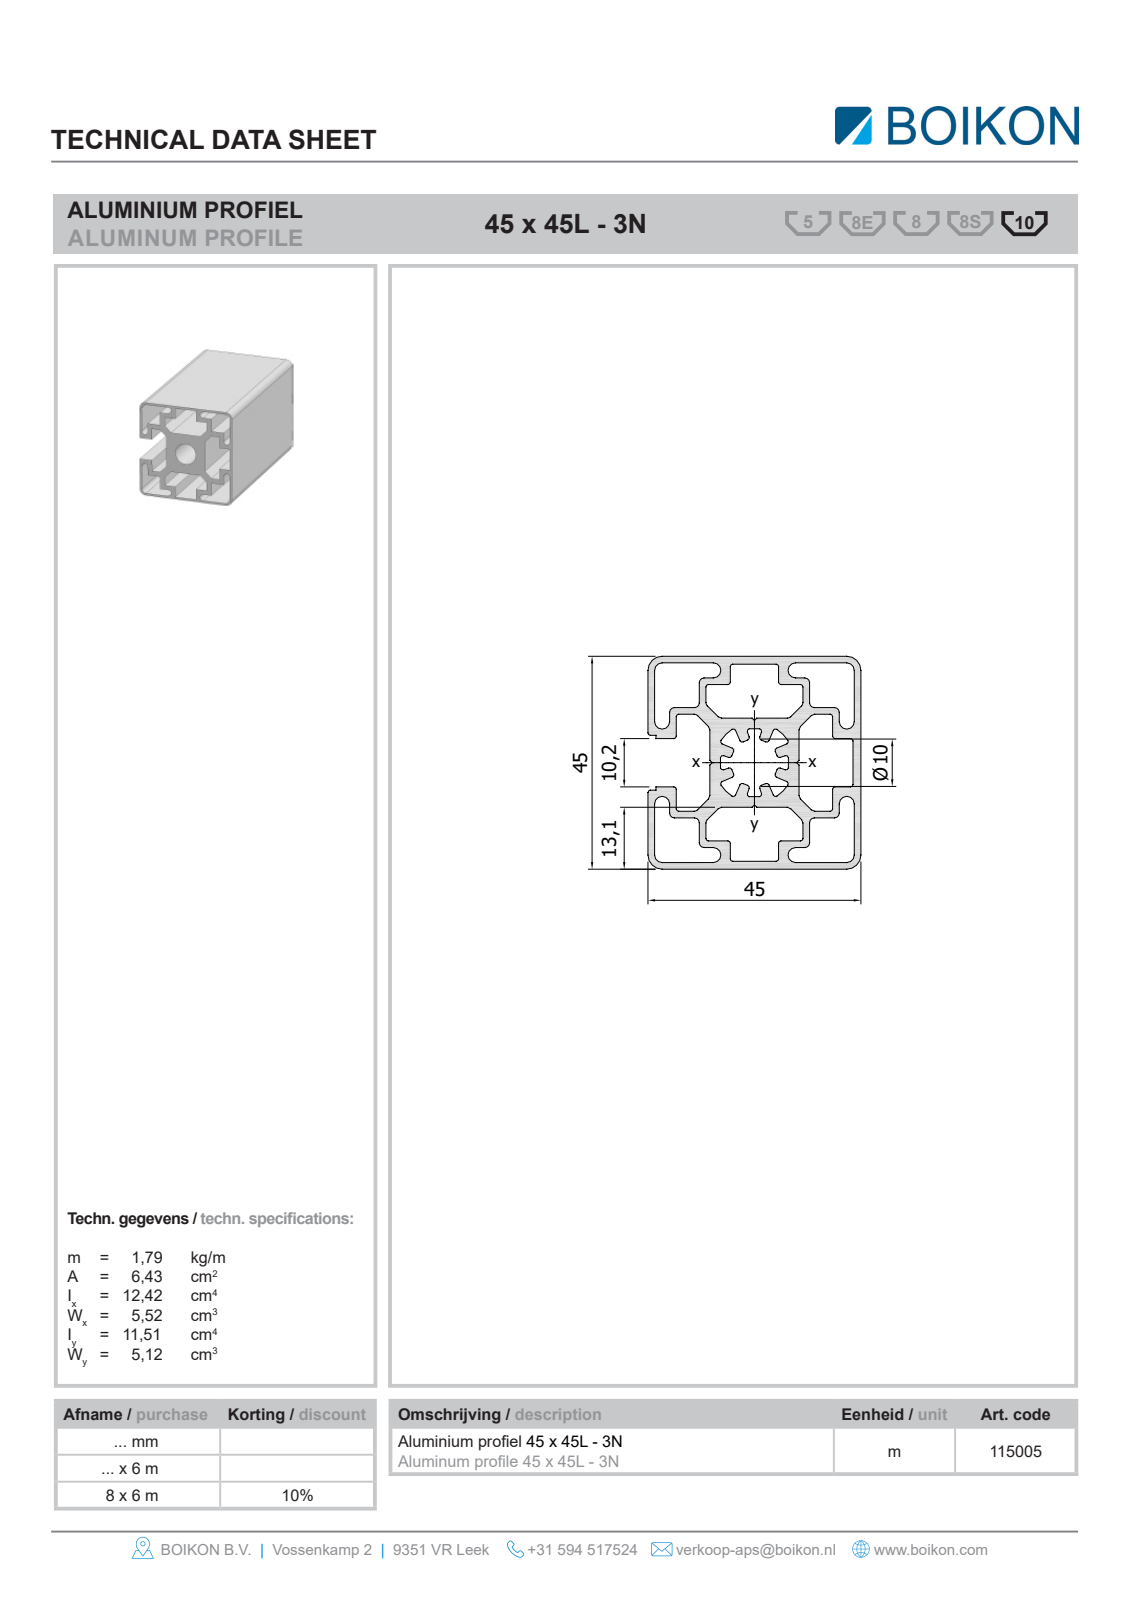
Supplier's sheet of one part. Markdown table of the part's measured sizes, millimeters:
| quantity | value |
| --- | --- |
| part name | Root; 11500545x45L-3NBOIKON0 |
| STEP written by | HiCAD 2013 1802.4 Build 509 (AUTOMOTIVE_DESIGN) |
| units | millimeters |
| bodies | 1 solid, 71 faces (62 planar, 9 cylindrical, 0 other) |
| overall size | 1000 × 45 × 45 |
| volume | 860 208 mm³ |
| surface area | 576 425 mm² |
| round holes (diameter × count) | 10 × 1 |
| partial cylindrical surfaces (radius × count) | 2 × 4, 3 × 4 |
| main face-to-face distances | 1, 44, 10, 35, 34, 9, 45, 13.1, 3.1, 31.9 |
